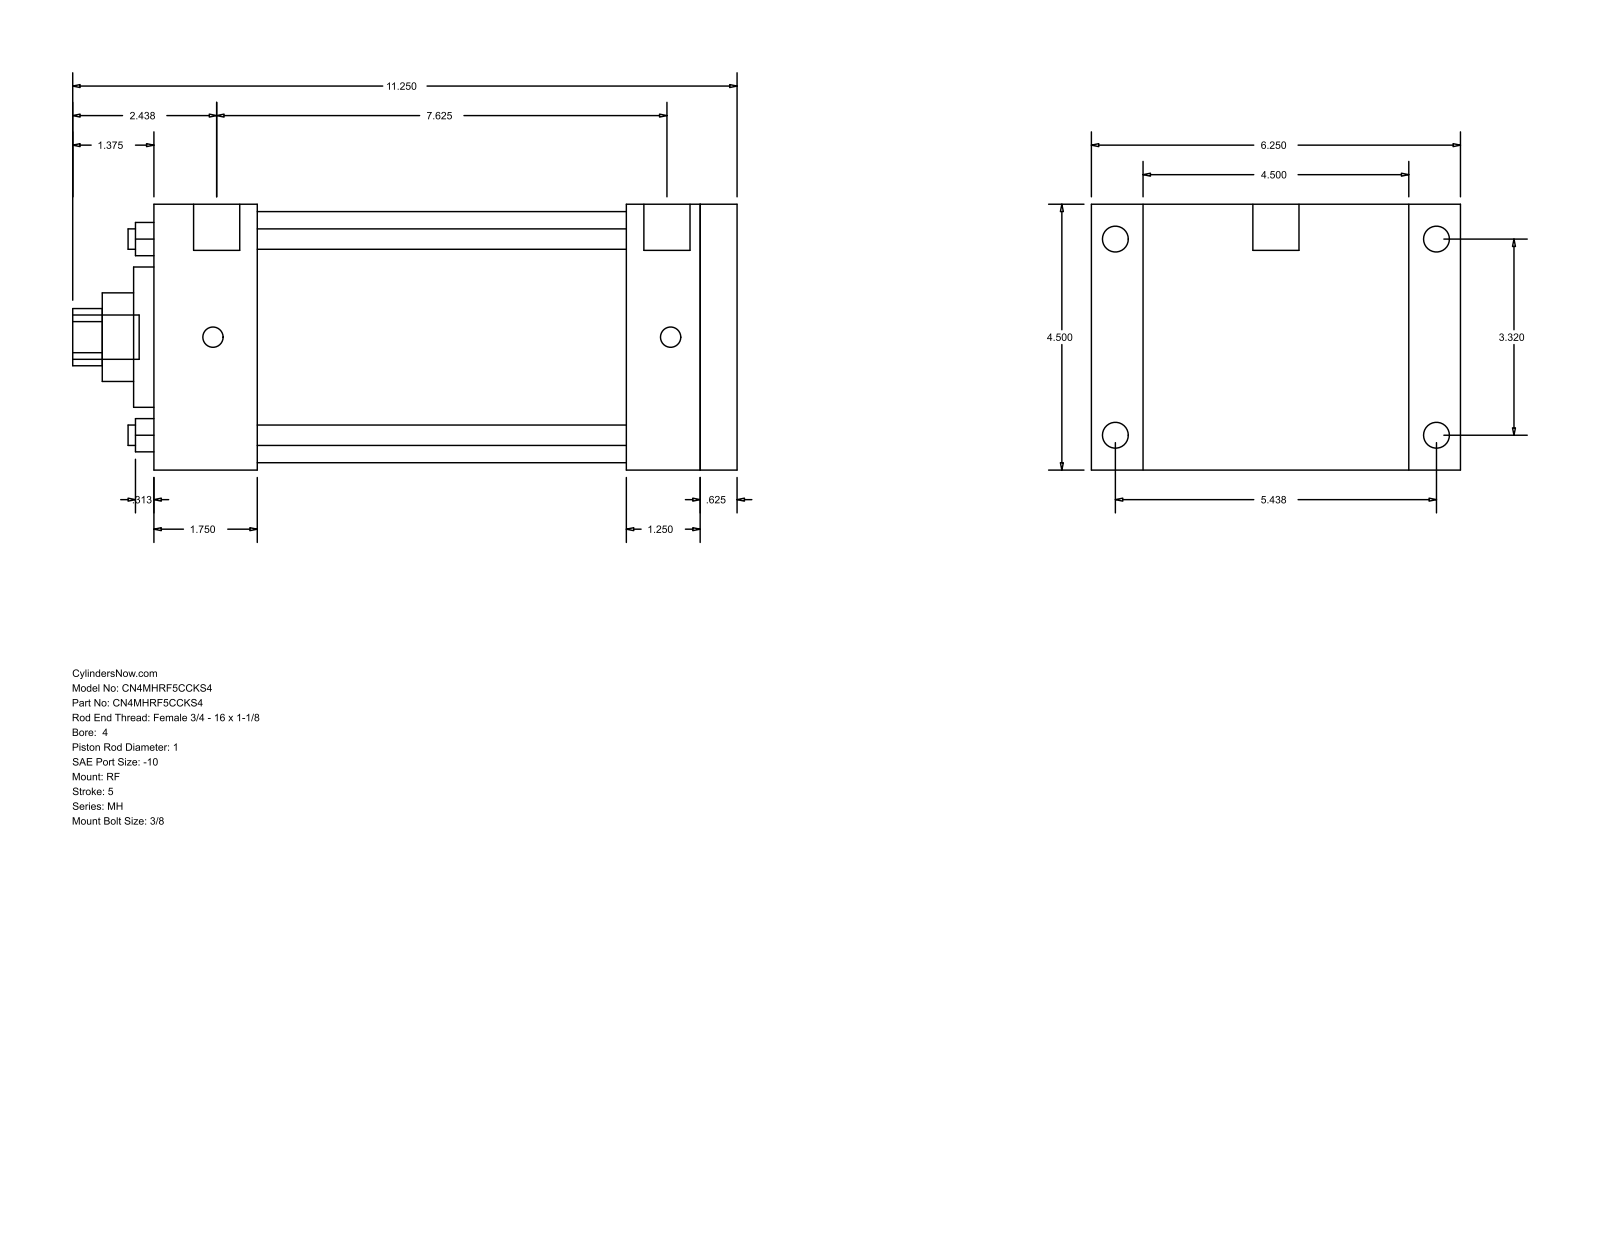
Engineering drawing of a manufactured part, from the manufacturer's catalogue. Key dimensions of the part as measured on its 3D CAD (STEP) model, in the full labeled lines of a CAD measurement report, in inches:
Part name (STEP PRODUCT): MH_RF__0400_1
STEP written by: GSSL Pune (CONFIG_CONTROL_DESIGN)
Units: inches
Bodies: 0 solids, 94 faces (65 planar, 29 cylindrical, 0 other)
Overall size (bounding box): 11.25 × 6.25 × 4.5
Round holes (diameter × count): ⌀0.345 ×4, ⌀1 ×1, ⌀1.5 ×1, ⌀2.375 ×1, ⌀4.25 ×1
Round bosses / shafts (diameter × count): ⌀0.438 ×4, ⌀0.344 ×4, ⌀0.781 ×2, ⌀0.75 ×1
Partial cylindrical surfaces — rounded edges, fillets, slot ends (radius × count): R0.484 ×1
Main face-to-face distances: 4.5, 9.875, 0.625, 9.25, 1.875, 1.75, 7.5, 8.125, 8, 6.25
Hole centre spacings: 2.347, 3.32, 4.695
